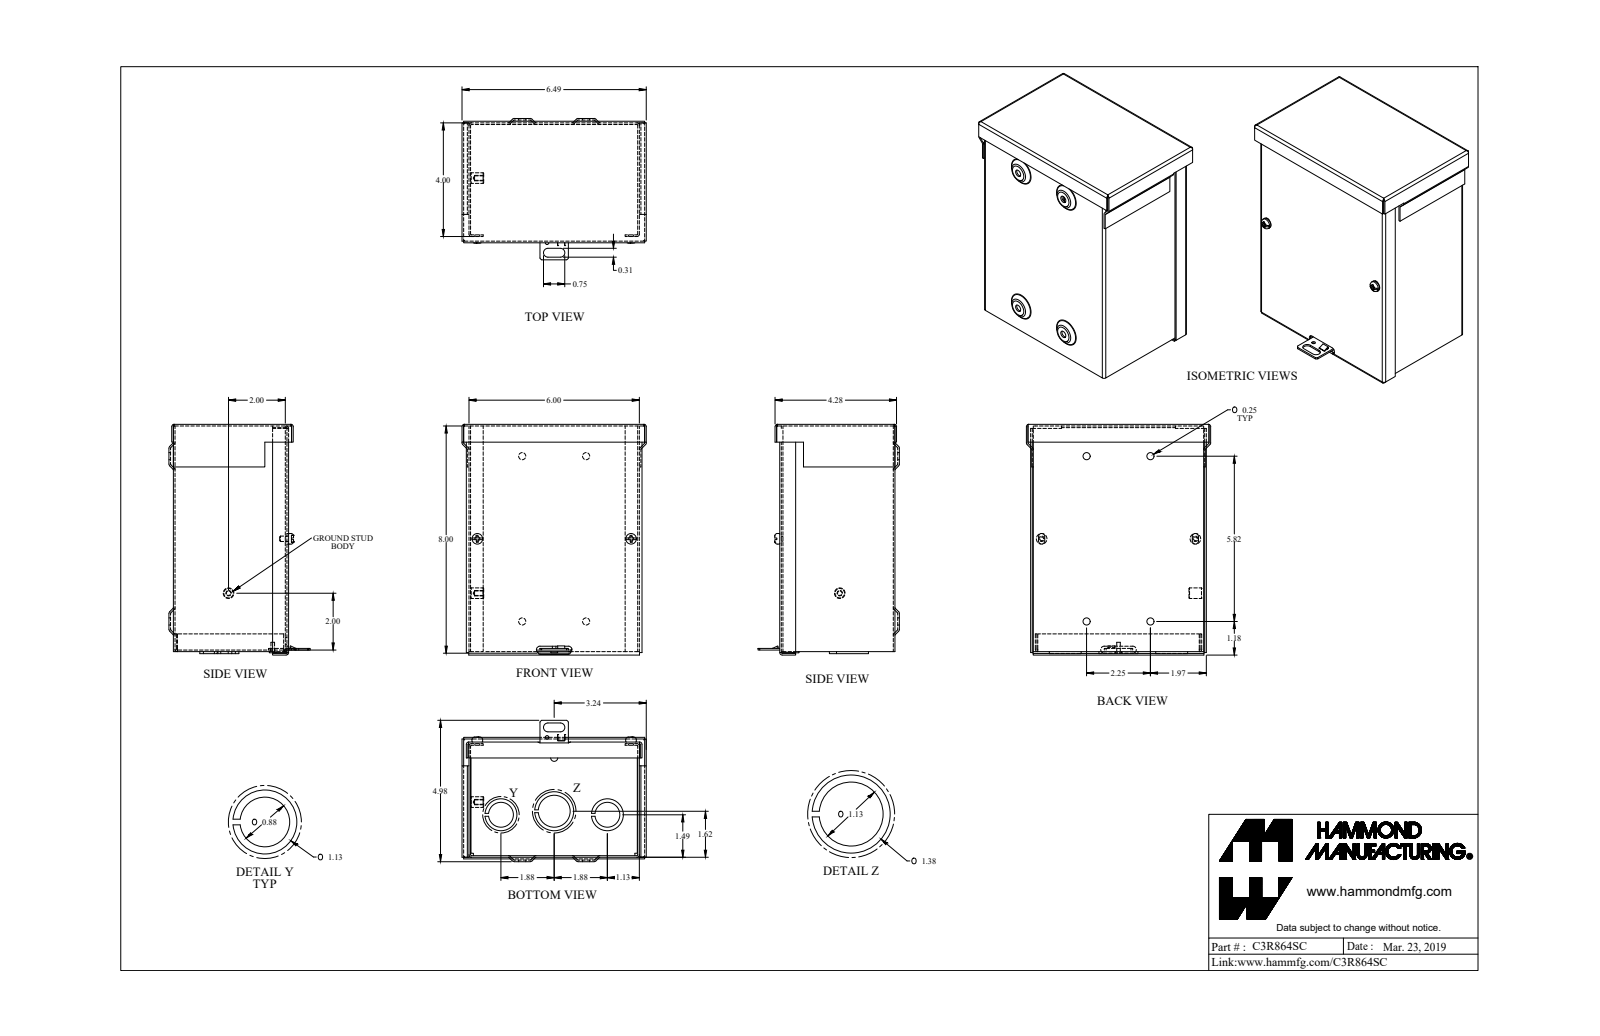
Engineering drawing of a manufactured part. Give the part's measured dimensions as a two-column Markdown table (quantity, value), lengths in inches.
| quantity | value |
| --- | --- |
| part name | C3R864SC_Default |
| STEP written by | SolidWorks 2019 (CONFIG_CONTROL_DESIGN) |
| units | inches |
| bodies | 9 solids, 353 faces (182 planar, 97 cylindrical, 74 other) |
| overall size | 8.12 × 6.489 × 4.977 |
| volume | 14.81 in³ |
| surface area | 525.8 in² |
| round holes (diameter × count) | 0.25 × 4, 0.17 × 2, 0.875 × 2, 0.125 × 1, 0.137 × 1, 0.156 × 1, 1.125 × 1 |
| round bosses / shafts (diameter × count) | 1.125 × 2, 0.375 × 2, 0.19 × 2, 1.375 × 1, 0.375 × 1, 0.125 × 1 |
| partial cylindrical surfaces (radius × count) | 0.029 × 21, 0.086 × 21, 0.125 × 8, 0.109 × 4, 0.156 × 2 |
| main face-to-face distances | 0.057, 4, 5.943, 3.943, 4.057, 0.057, 6, 5.886, 7.886, 7.943 |
| hole center spacings | 3.311, 4.811, 2.25, 5.818, 6.238, 0.763, 1.879, 1.88 |
